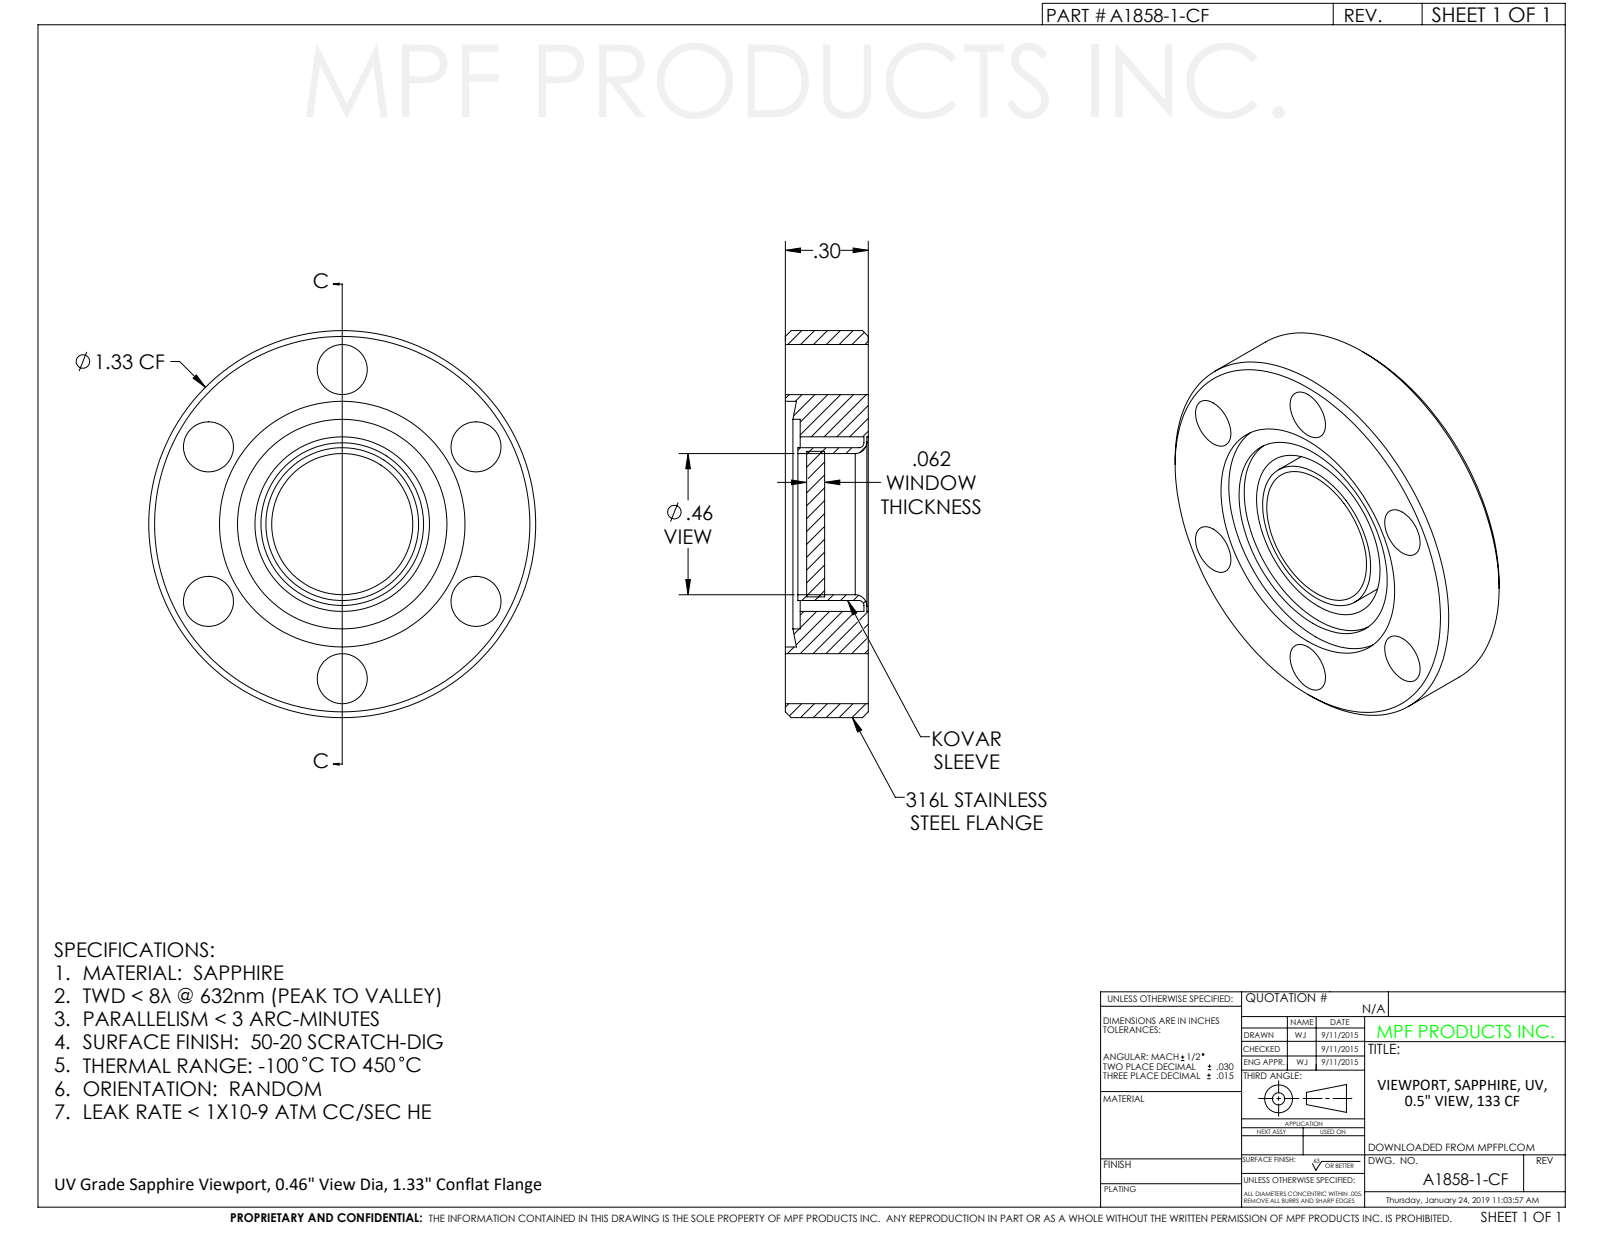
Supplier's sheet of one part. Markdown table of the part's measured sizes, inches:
| quantity | value |
| --- | --- |
| part name | A1858-1-CF |
| STEP written by | SolidWorks 2011 (CONFIG_CONTROL_DESIGN) |
| units | inches |
| bodies | 1 solid, 54 faces (10 planar, 32 cylindrical, 12 other) |
| overall size | 1.33 × 1.33 × 0.285 |
| volume | 0.278 in³ |
| surface area | 5.915 in² |
| round holes (diameter × count) | 0.172 × 6, 0.485 × 1, 0.505 × 1, 0.6 × 1, 0.67 × 1, 0.72 × 1, 0.743 × 1, 0.844 × 1 |
| round bosses / shafts (diameter × count) | 1.33 × 1, 0.74 × 1, 0.525 × 1 |
| main face-to-face distances | 0.285, 0.135, 0.212, 0.073, 0.15, 0.062, 0.145, 0.207, 0.28, 0.234 |
| hole center spacings | 0.531, 0.92, 0.531, 1.062, 1.062 |
